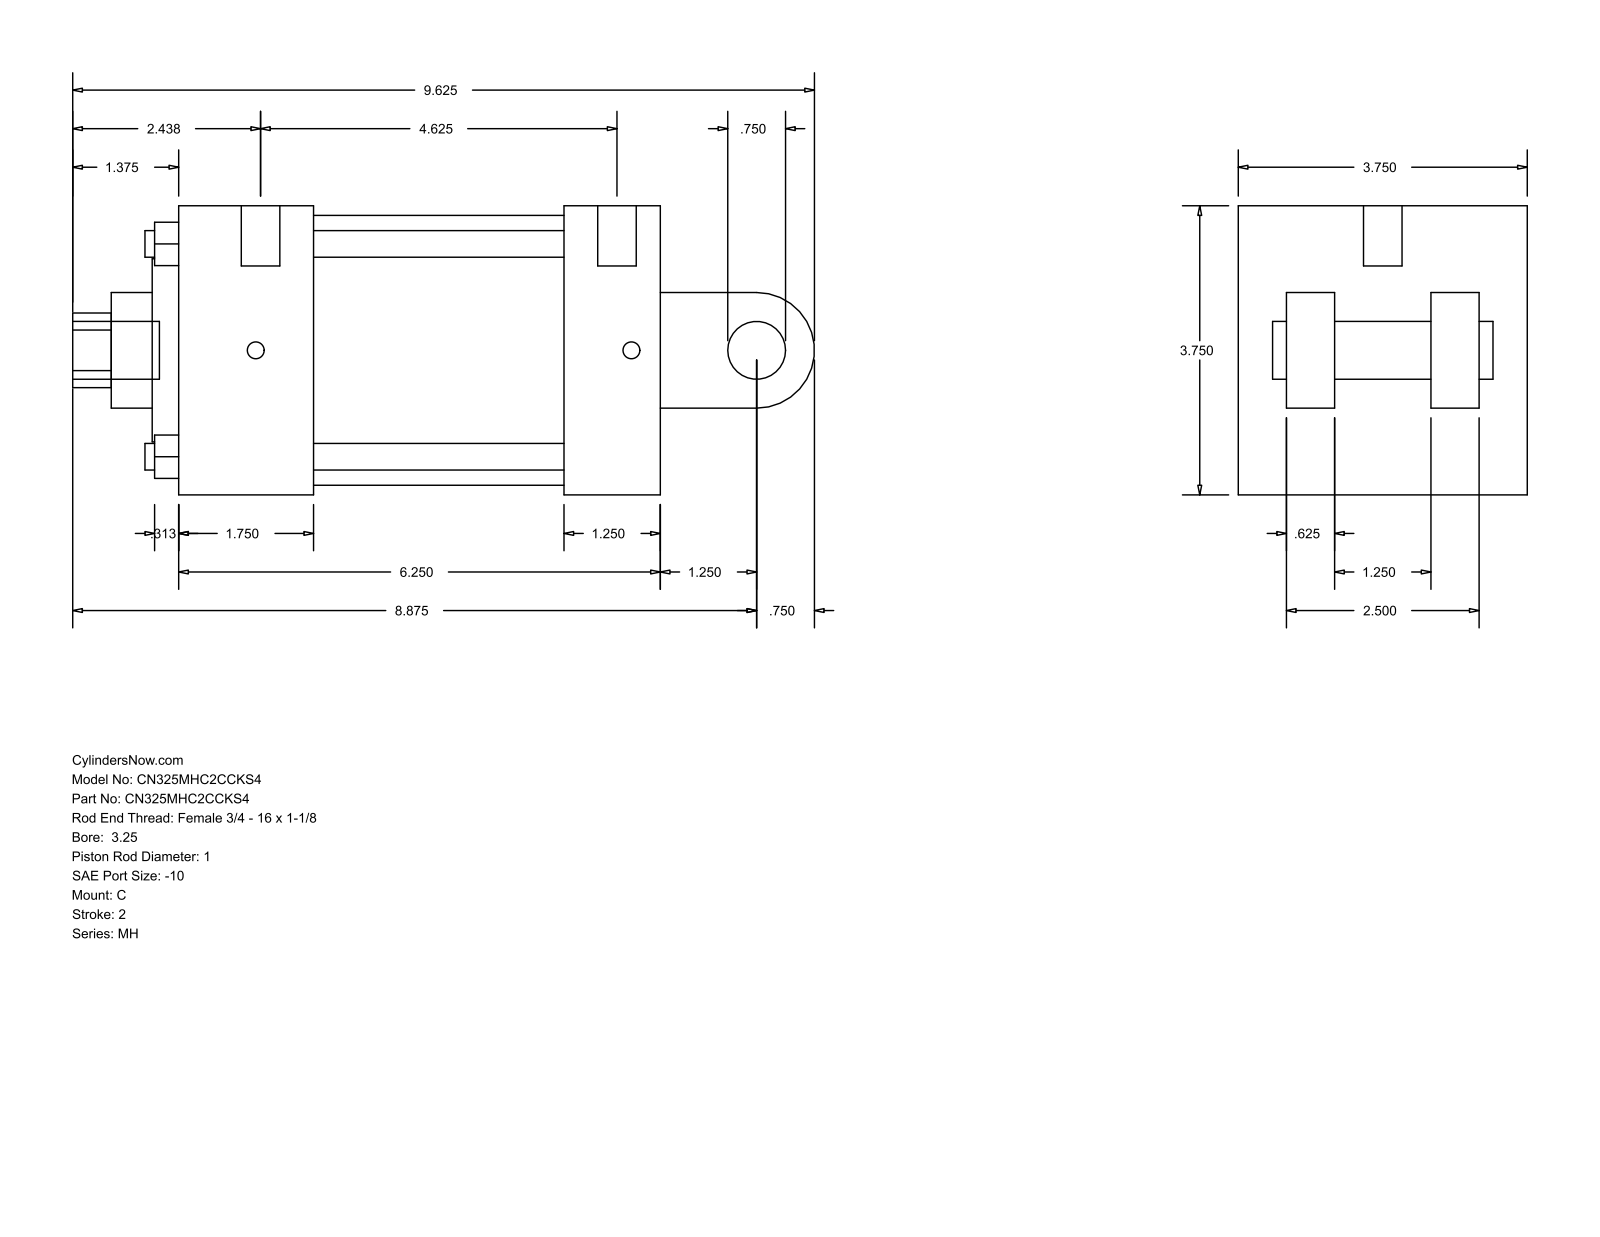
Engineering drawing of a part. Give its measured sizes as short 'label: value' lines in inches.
name: MH_C__0325_1
written by: GSSL Pune (CONFIG_CONTROL_DESIGN)
unit: in
bodies: 0 solids, 101 faces (71 planar, 30 cylindrical, 0 other)
size: 9.625 × 3.75 × 3.75
holes: 4× ⌀0.345, 2× ⌀0.219, 1× ⌀0.5, 1× ⌀1, 1× ⌀1.5, 1× ⌀2.375, 1× ⌀3.5
bosses: 2× ⌀0.75, 2× ⌀0.219, 1× ⌀0.5
rounds: 1× R0.484, 1× R0.75
face distances: 3.75, 0.625, 6.25, 2.5, 3.125, 1.25, 1.875, 1.75, 5, 3.25
hole spacings: 1.952, 2.76, 3.903, 0.187
